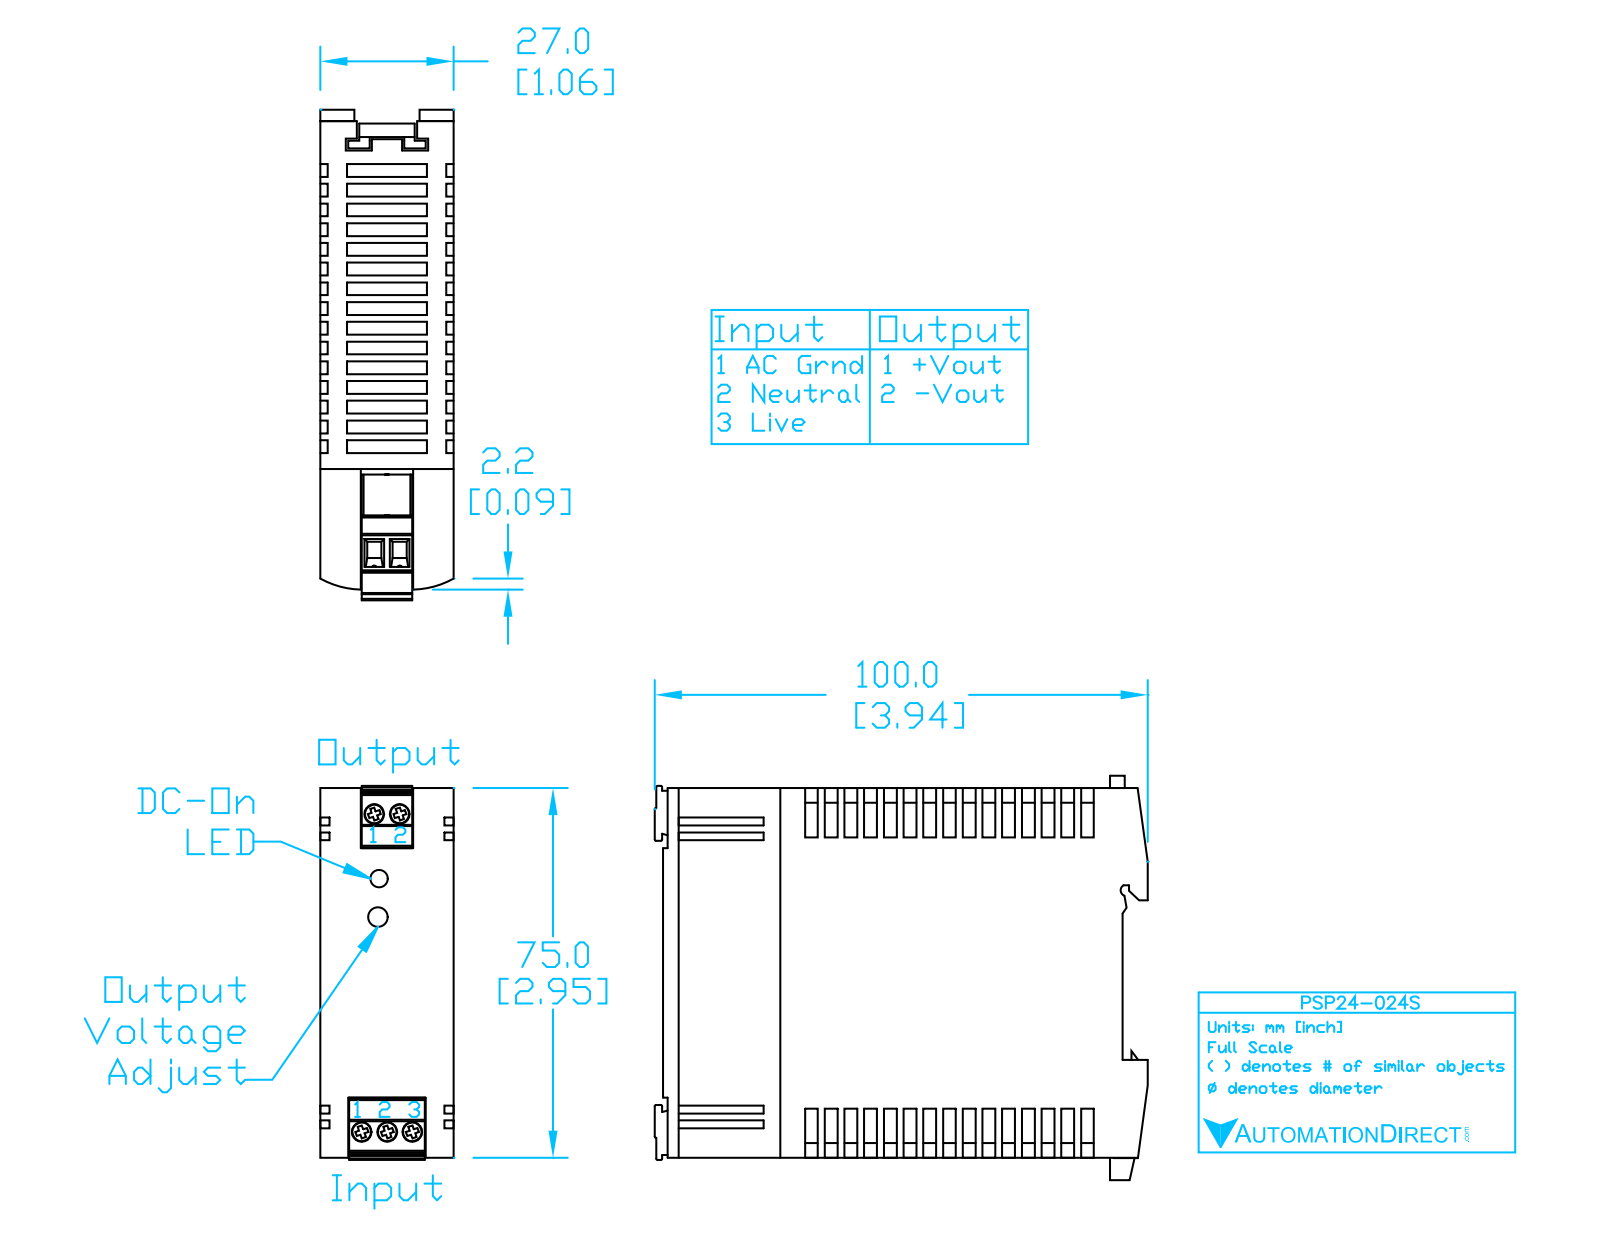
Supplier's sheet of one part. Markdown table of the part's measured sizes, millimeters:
| quantity | value |
| --- | --- |
| part name | PSP24-024S |
| STEP written by | SolidWorks 2011 (CONFIG_CONTROL_DESIGN) |
| units | millimeters |
| bodies | 1 solid, 236 faces (188 planar, 0 cylindrical, 48 other) |
| overall size | 102.25 × 80 × 27 |
| volume | 195 655 mm³ |
| surface area | 29 365 mm² |
| main face-to-face distances | 27, 75, 1, 5.25, 21.75, 11.85, 12.85, 51.5, 0.35, 63.35 |
